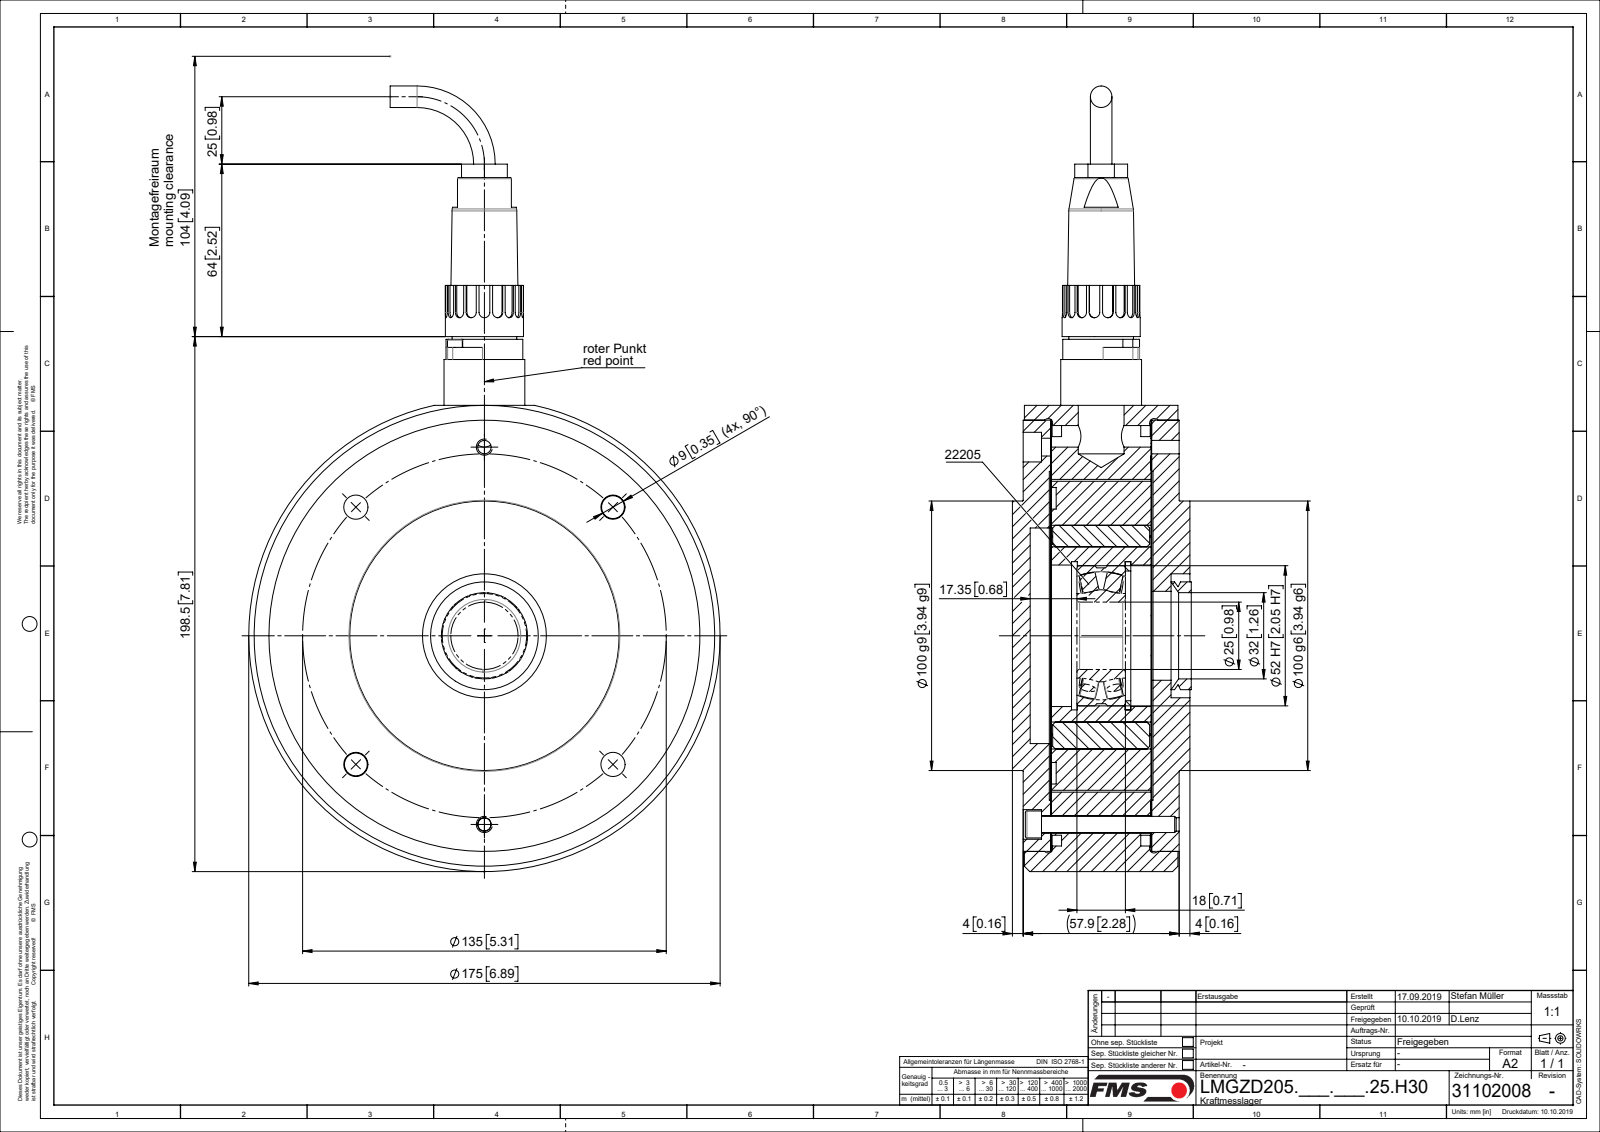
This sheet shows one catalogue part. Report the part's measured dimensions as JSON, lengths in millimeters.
{"part_name": "L48744; L4914704; TEIL1; L49024 (+8 more)", "step_written_by": "Mechanical Desktop 2007 (CONFIG_CONTROL_DESIGN)", "units": "millimeters", "bodies": {"solids": 17, "faces": 377, "planar": 118, "cylindrical": 215, "other": 44}, "overall_size": [291.5, 175, 66.4], "volume_mm3": 1356000, "surface_area_mm2": 265834, "round_holes": [[9, 4], [2.6, 2], [3, 2], [3.6, 2], [5, 2], [6.6, 2], [8.68, 2], [11, 2], [10.5, 1], [14, 1], [22, 1], [25, 1]], "round_bosses_or_shafts": [[5.5, 2], [175, 1], [160, 1], [148, 1], [100, 1], [39, 1], [29, 1], [28.5, 1]], "partial_cylinders_radius": [[2, 18], [3, 2], [7.5, 2]], "face_to_face_distances": [37.25, 10.2, 10.45, 47.45, 47.7, 37, 37.5, 38, 9.7, 48.2], "hole_center_spacings": [52.67, 67.5, 95.46, 127.04, 16.26, 70, 135, 32.53]}
